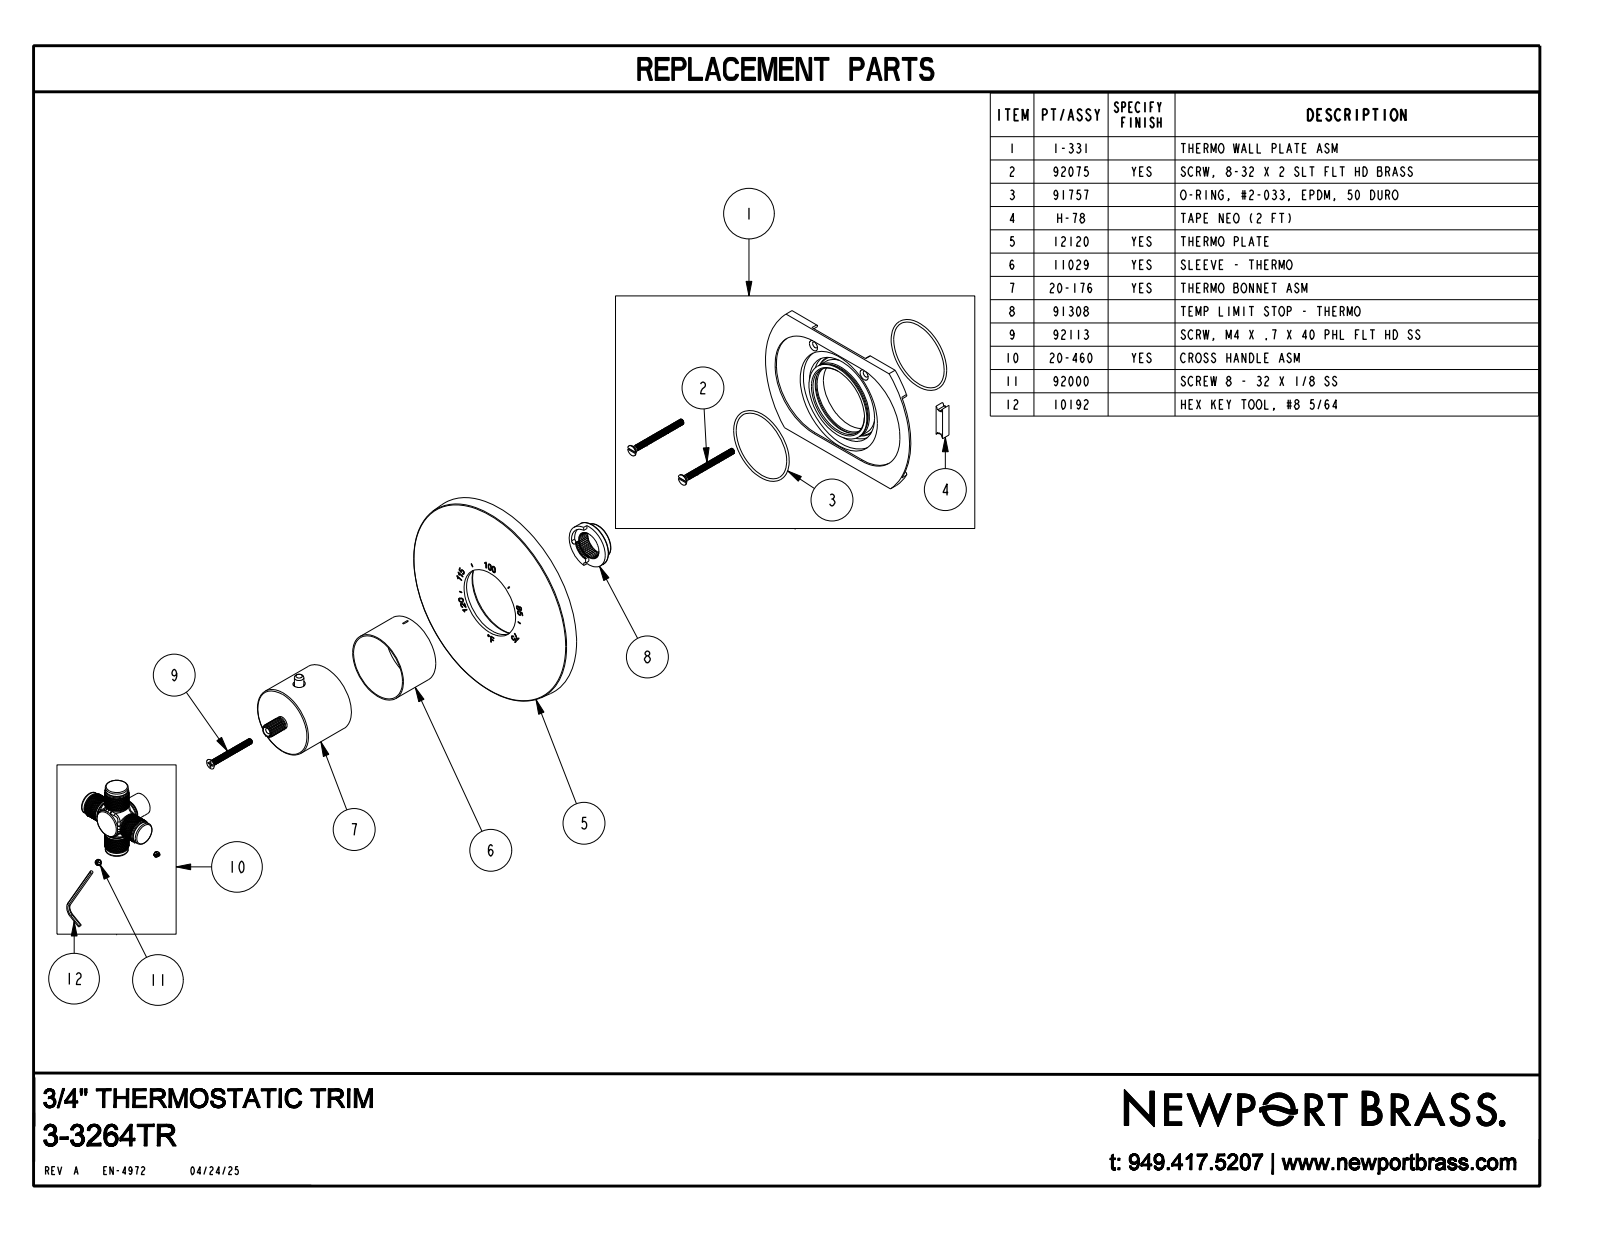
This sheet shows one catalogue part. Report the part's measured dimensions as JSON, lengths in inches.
{"part_name": "12120; 11029; 12541; 11555 (+8 more)", "step_written_by": "CREO PARAMETRIC BY PTC INC, 2018400 (CONFIG_CONTROL_DESIGN)", "units": "inches", "bodies": {"solids": 15, "faces": 15476, "planar": 532, "cylindrical": 2923, "other": 12021}, "overall_size": [6, 5.994, 4.558], "volume_in3": 6.219, "surface_area_in2": 211.4, "round_holes": [[0.136, 2], [0.25, 2], [0.403, 2], [0.47, 2], [0.063, 1], [0.118, 1], [0.17, 1], [0.276, 1], [0.28, 1], [0.339, 1], [0.43, 1], [1.83, 1]], "round_bosses_or_shafts": [[0.37, 3], [0.67, 2], [0.63, 2], [0.433, 2], [0.164, 2], [2.5, 1], [1.97, 1], [1.28, 1]], "partial_cylinders_radius": [[0.03, 4], [0.075, 2], [0.086, 2], [0.188, 2], [0.02, 1], [0.055, 1], [0.164, 1], [0.187, 1]], "face_to_face_distances": [0.09, 2.613, 2.523, 2.533, 2.443, 0.08, 0.1, 2.543, 2.623, 0.275], "hole_center_spacings": [0.632, 1.685]}
